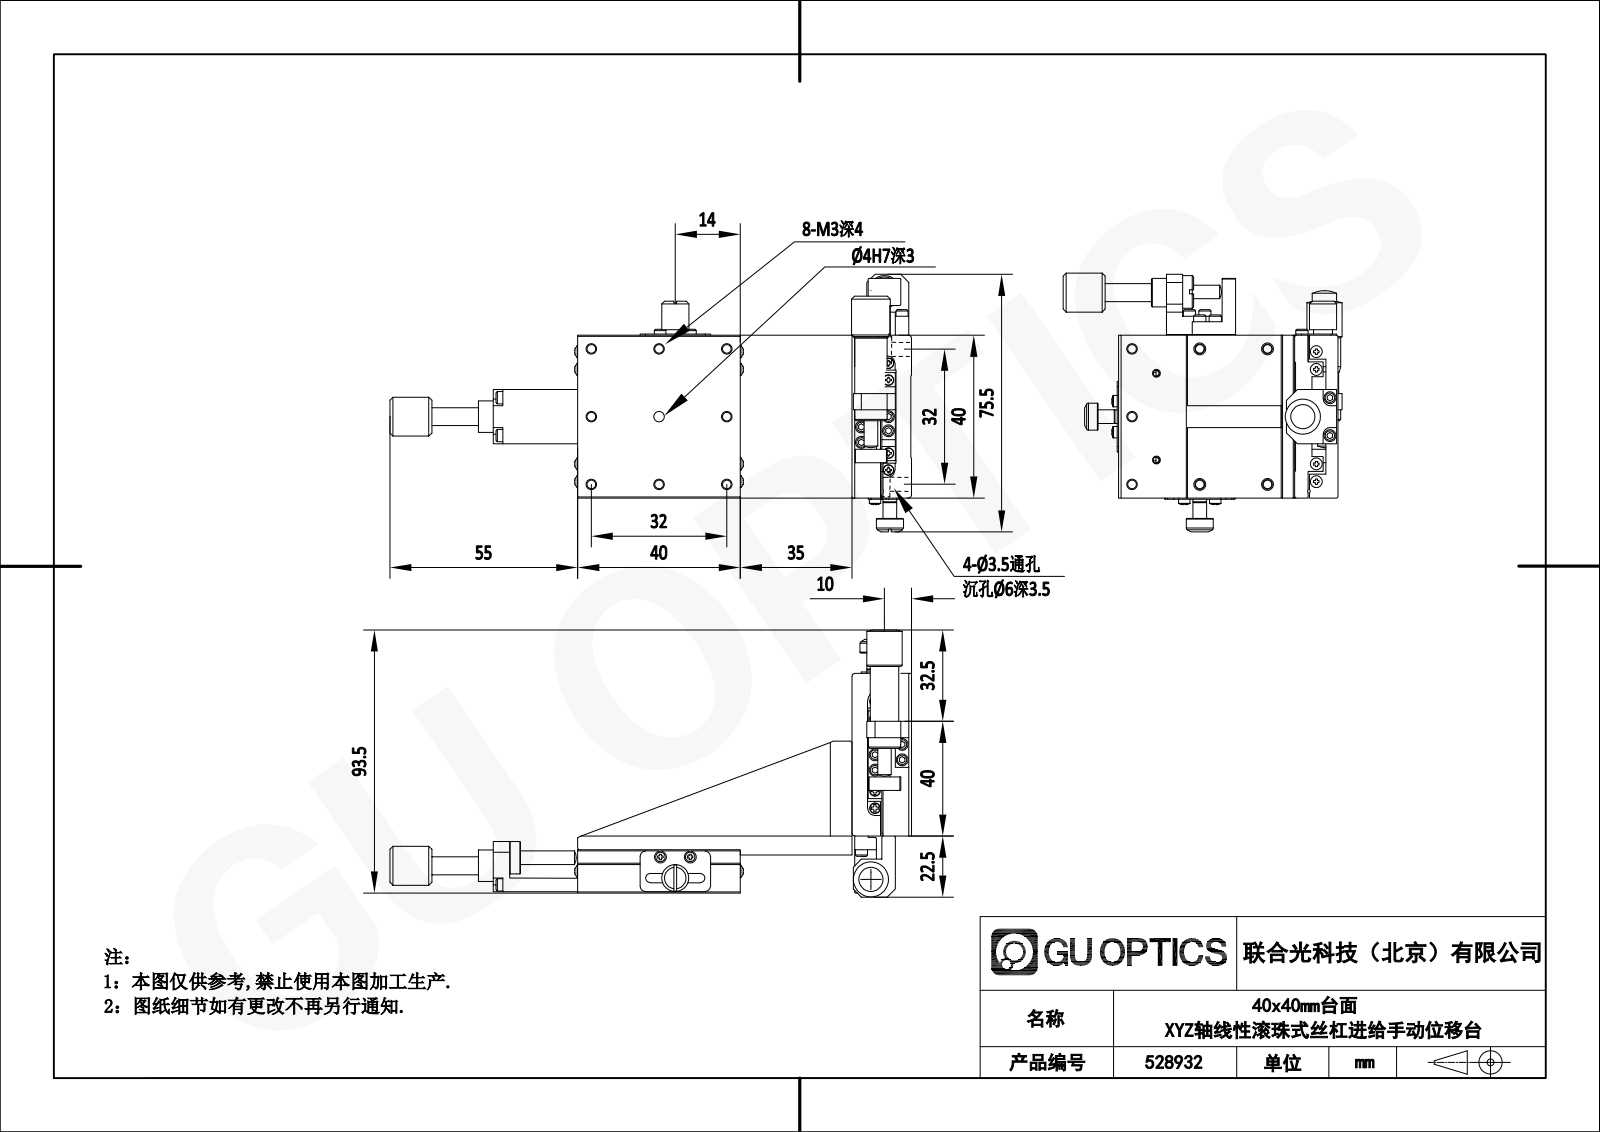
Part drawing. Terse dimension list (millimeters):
name: 528932
written by: SolidWorks 2020 (CONFIG_CONTROL_DESIGN)
unit: mm
bodies: 8 solids, 2558 faces (1458 planar, 363 cylindrical, 737 other)
size: 152.05 × 95 × 74.3
volume: 104 127 mm³; area: 54 676 mm²
holes: 14× ⌀2.46, 10× ⌀6, 8× ⌀3.5, 6× ⌀2.85, 2× ⌀2.01, 2× ⌀2.01, 2× ⌀2.46, 2× ⌀3.96, 2× ⌀4, 1× ⌀3.24, 1× ⌀5
bosses: 16× ⌀4.5, 4× ⌀4.2, 4× ⌀4, 3× ⌀12, 3× ⌀7, 3× ⌀6, 3× ⌀3, 2× ⌀9.5
rounds: 34× R0.25, 24× R0.1, 12× R2, 8× R0.5, 8× R1, 4× R1.65, 2× R1.4, 2× R1.75
face distances: 5, 16, 5.5, 11, 10.5, 5.7, 0.5, 40, 10.3, 6
hole spacings: 16, 22.63, 35.78, 32, 45.25, 20, 32.25, 46.82
